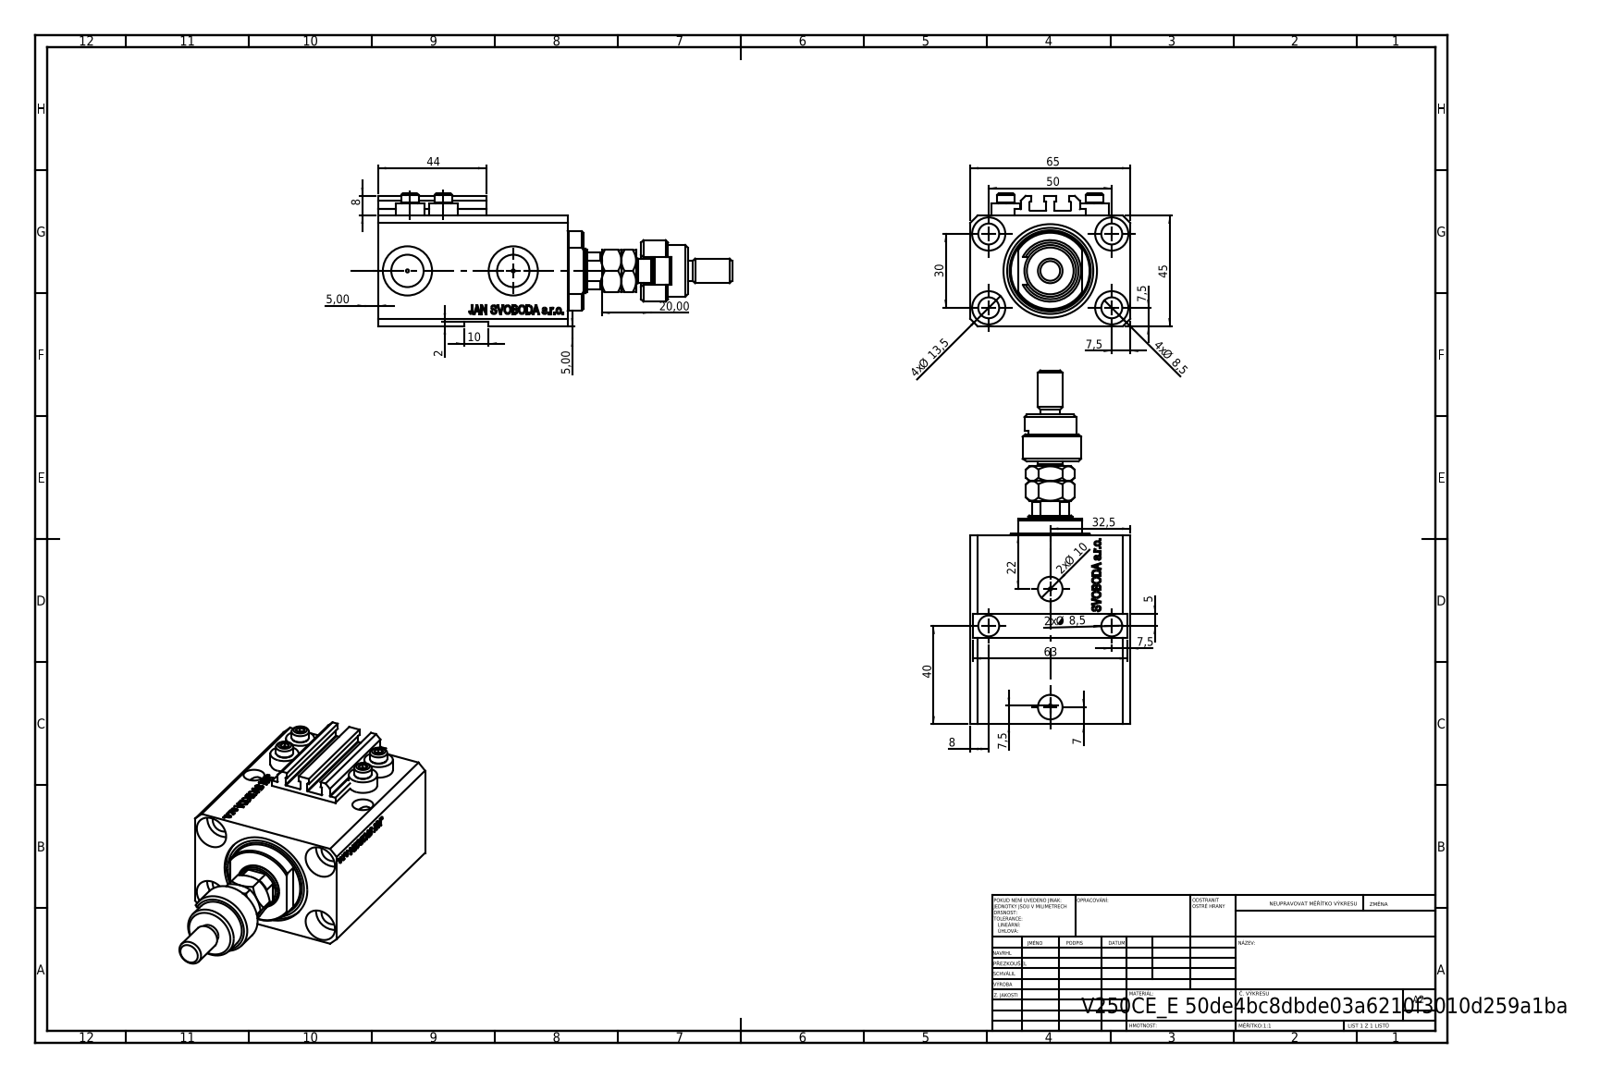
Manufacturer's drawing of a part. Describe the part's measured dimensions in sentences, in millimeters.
The part is named "ALLEN BOLT V250CE; FEMALE_PART_FOR_DFA; V250CE_C_VCP; V250CE_E_Body (+2 more)". Its 3-D file was written by "SolidWorks 2019 (CONFIG_CONTROL_DESIGN)". It is 10 solids with 1152 faces: 539 planar, 139 cylindrical and 474 other. Overall it measures 143.9 by 65 by 54 millimeters. Its volume is 211 560 cubic millimeters and its surface area 66 736 square millimeters. Round holes: 7 of diameter 8.5, 4 of diameter 1.25, 4 of diameter 4, 4 of diameter 13.5, 2 of diameter 10, 2 of diameter 13.16, 2 of diameter 20, 1 of diameter 18, 1 of diameter 38. Round bosses or shafts: 4 of diameter 11.6, 4 of diameter 7, 1 of diameter 25, 1 of diameter 21, 1 of diameter 16, 1 of diameter 10, 1 of diameter 8. Partial cylindrical surfaces (rounded edges, fillets, slot ends): 10 of radius 0.2, 1 of radius 5.5, 1 of radius 8.5, 1 of radius 8.75, 1 of radius 16. The main face-to-face distances are 45, 65, 51.9, 77, 25.1, 2, 6.9, 3, 70.1, 9. The hole center spacings are 29.15, 50, 13.6, 15.12, 18.81, 18.97, 26.22, 26.61.
